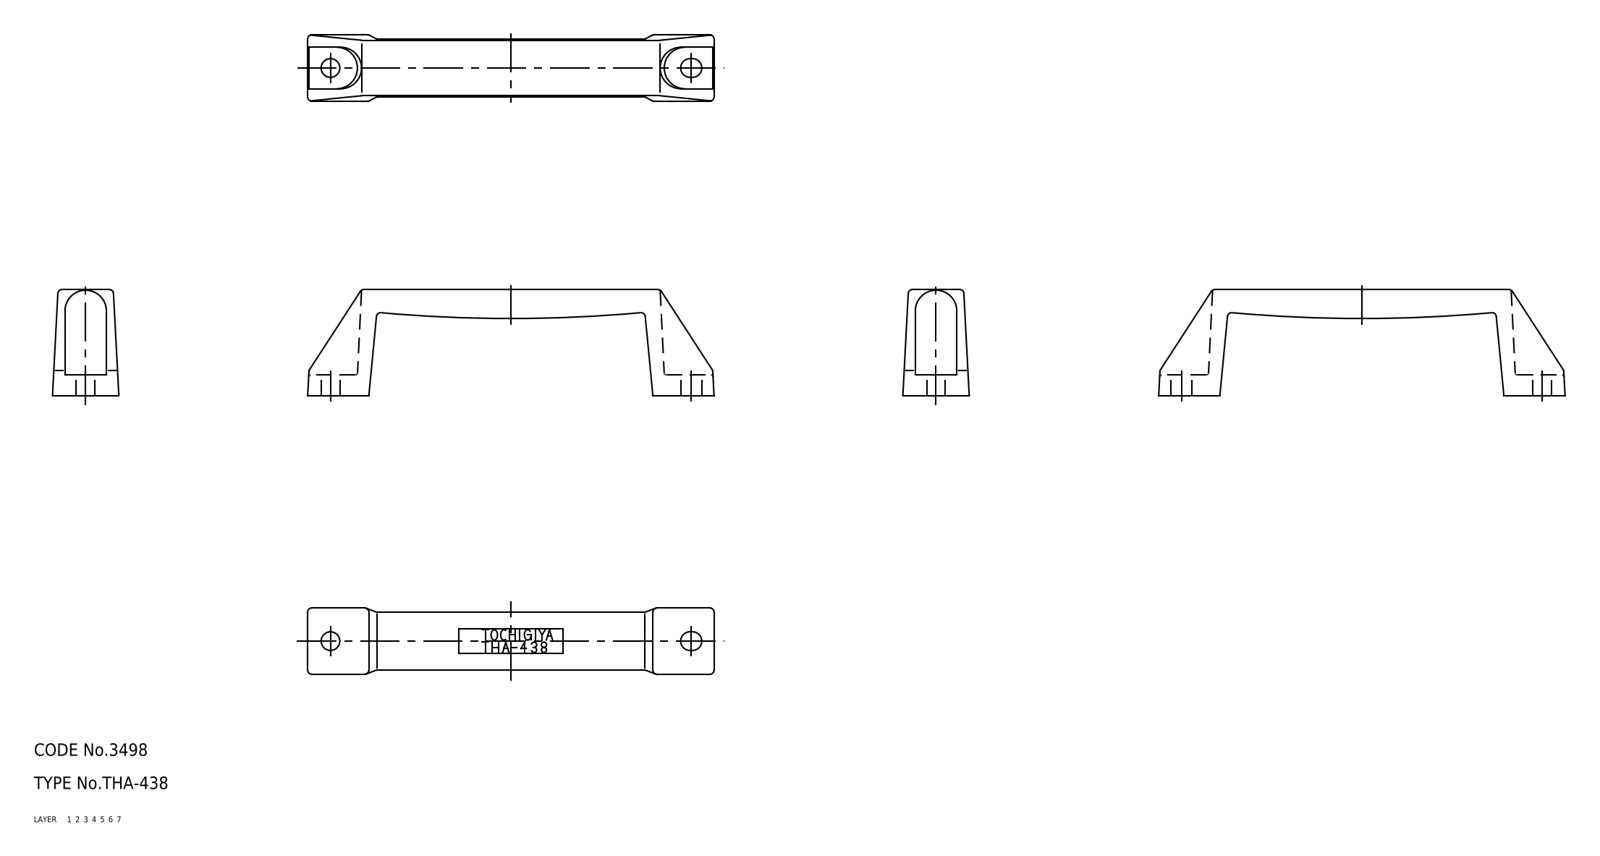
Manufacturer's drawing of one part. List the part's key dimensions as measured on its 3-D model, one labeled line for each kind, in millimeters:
Part name (STEP PRODUCT): pull
STEP written by: CADfix (AUTOMOTIVE_DESIGN)
Units: millimetres
Bodies: 1 solid, 76 faces (0 planar, 0 cylindrical, 76 other)
Overall size (bounding box): 98 × 25.6 × 16
Volume: 11 586 mm³ · Surface area: 6 098 mm²
